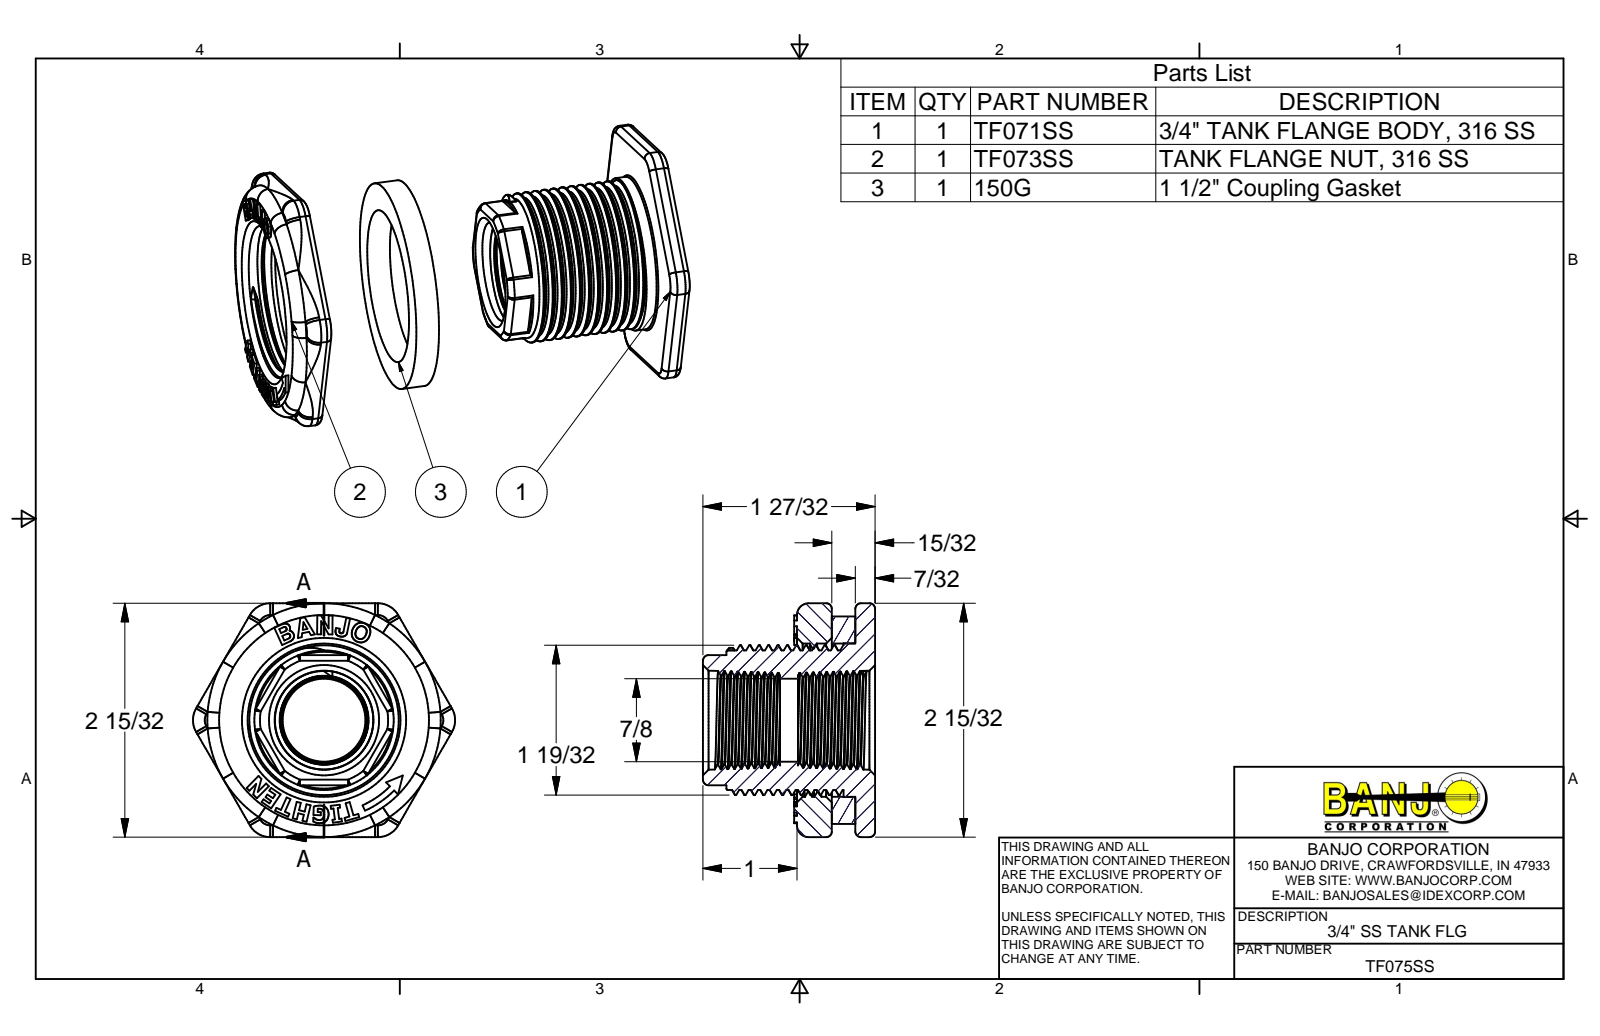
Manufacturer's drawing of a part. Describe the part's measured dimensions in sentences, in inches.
The part is named "TF075SS; TF071SS; TF073SS; 150G". Its 3-D file was written by "Autodesk Inventor 2013 (AUTOMOTIVE_DESIGN)". It is 3 solids with 403 faces: 173 planar, 72 cylindrical and 158 other. Overall it measures 2.786 by 2.48 by 1.83 inches. Its volume is 4.133 cubic inches and its surface area 47.79 square inches. Round holes: 1 of diameter 0.88, 1 of diameter 1.517, 1 of diameter 1.625. Round bosses or shafts: 1 of diameter 2.2, 1 of diameter 1.63, 1 of diameter 1.589, 1 of diameter 1.481. Partial cylindrical surfaces (rounded edges, fillets, slot ends): 36 of radius 0.06, 6 of radius 0.125, 6 of radius 0.25, 1 of radius 0.4, 1 of radius 0.991, 1 of radius 1.054. The main face-to-face distances are 0.25, 0.46, 0.21, 0.37, 0.62, 0.83, 0.55, 2.48, 1.93, 1.37.
